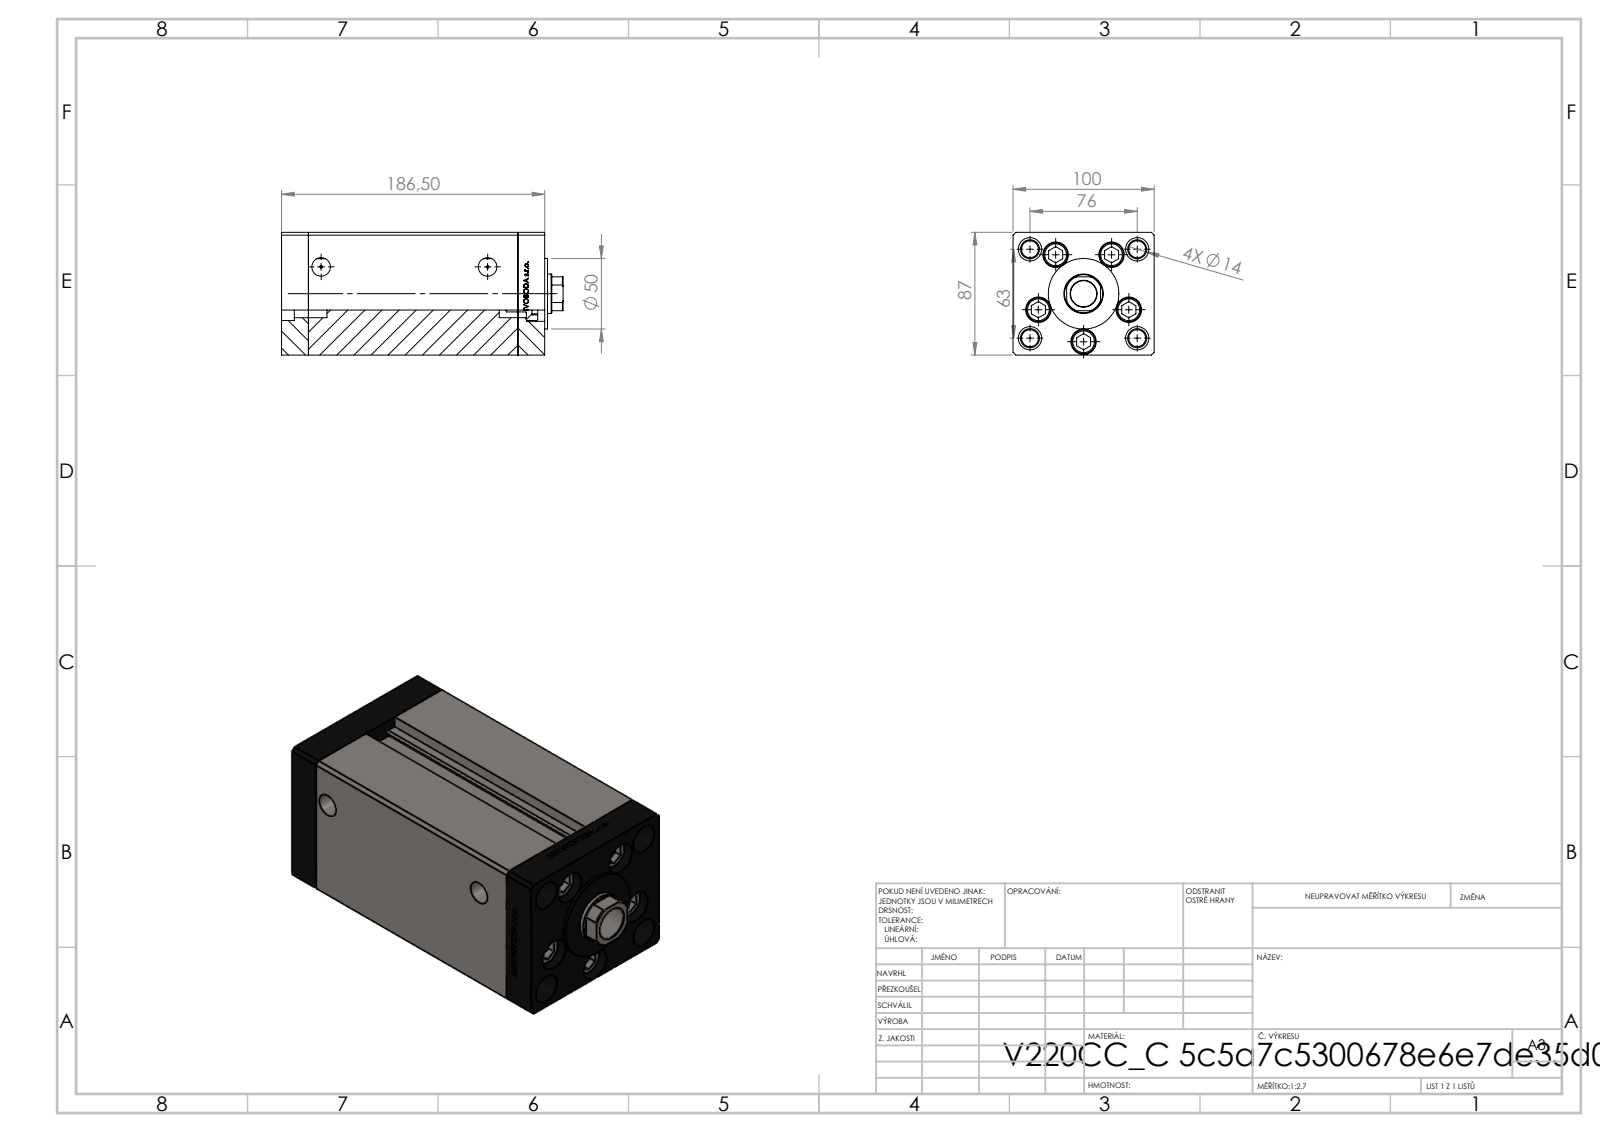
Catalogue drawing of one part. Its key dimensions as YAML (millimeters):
part_name: "V220C_VC_C; V220C FRONT; V220C_C MIDDLE; ALLEN BOLT (+1 more)"
step_written_by: "SolidWorks 2019 (CONFIG_CONTROL_DESIGN)"
units: millimeters
bodies: {solids: 13, faces: 1172, planar: 542, cylindrical: 168, other: 462}
overall_size: [199.5, 100, 87]
volume: 1332000
surface_area: 229693
round_holes:
  - {diameter: 13.5, count: 9}
  - {diameter: 18, count: 5}
  - {diameter: 12, count: 4}
  - {diameter: 16.5, count: 4}
  - {diameter: 2, count: 2}
  - {diameter: 13.16, count: 2}
  - {diameter: 17, count: 1}
  - {diameter: 18.5, count: 1}
  - {diameter: 28, count: 1}
round_bosses_or_shafts:
  - {diameter: 8, count: 5}
  - {diameter: 17, count: 4}
  - {diameter: 50, count: 1}
partial_cylinders:
  - {radius: 0.93, count: 2}
  - {radius: 13.5, count: 1}
face_to_face_distances: [100, 87, 19, 148.5, 167.5, 34.25, 186.5, 152.25, 133.25, 15.25]
hole_center_spacings: [34, 49.36, 18.59, 21.03, 38.08, 39.27, 40.83, 43.24]
